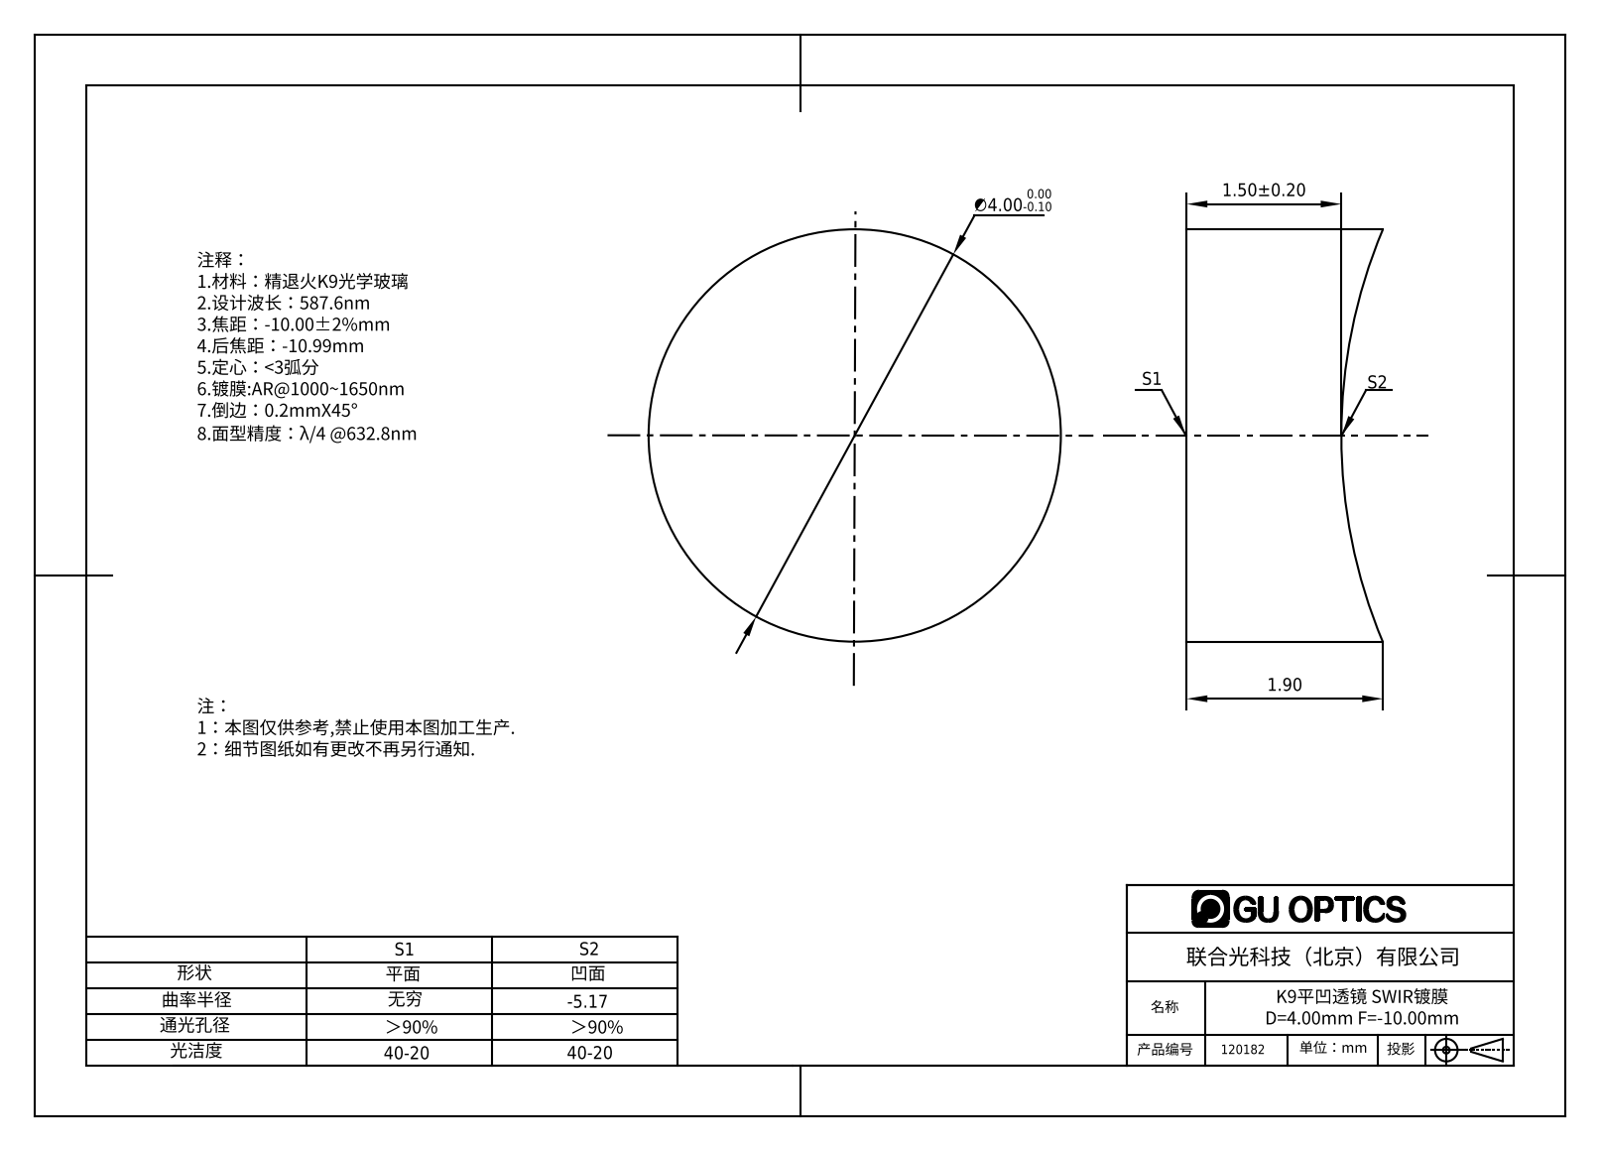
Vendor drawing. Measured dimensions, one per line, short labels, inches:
name: 120122
written by: SolidWorks 2016 (AUTOMOTIVE_DESIGN)
unit: in
bodies: 1 solid, 5 faces (1 planar, 2 cylindrical, 2 other)
size: 0.157 × 0.157 × 0.075
volume: 0.001 in³; area: 0.078 in²
bosses: 1× ⌀0.157
